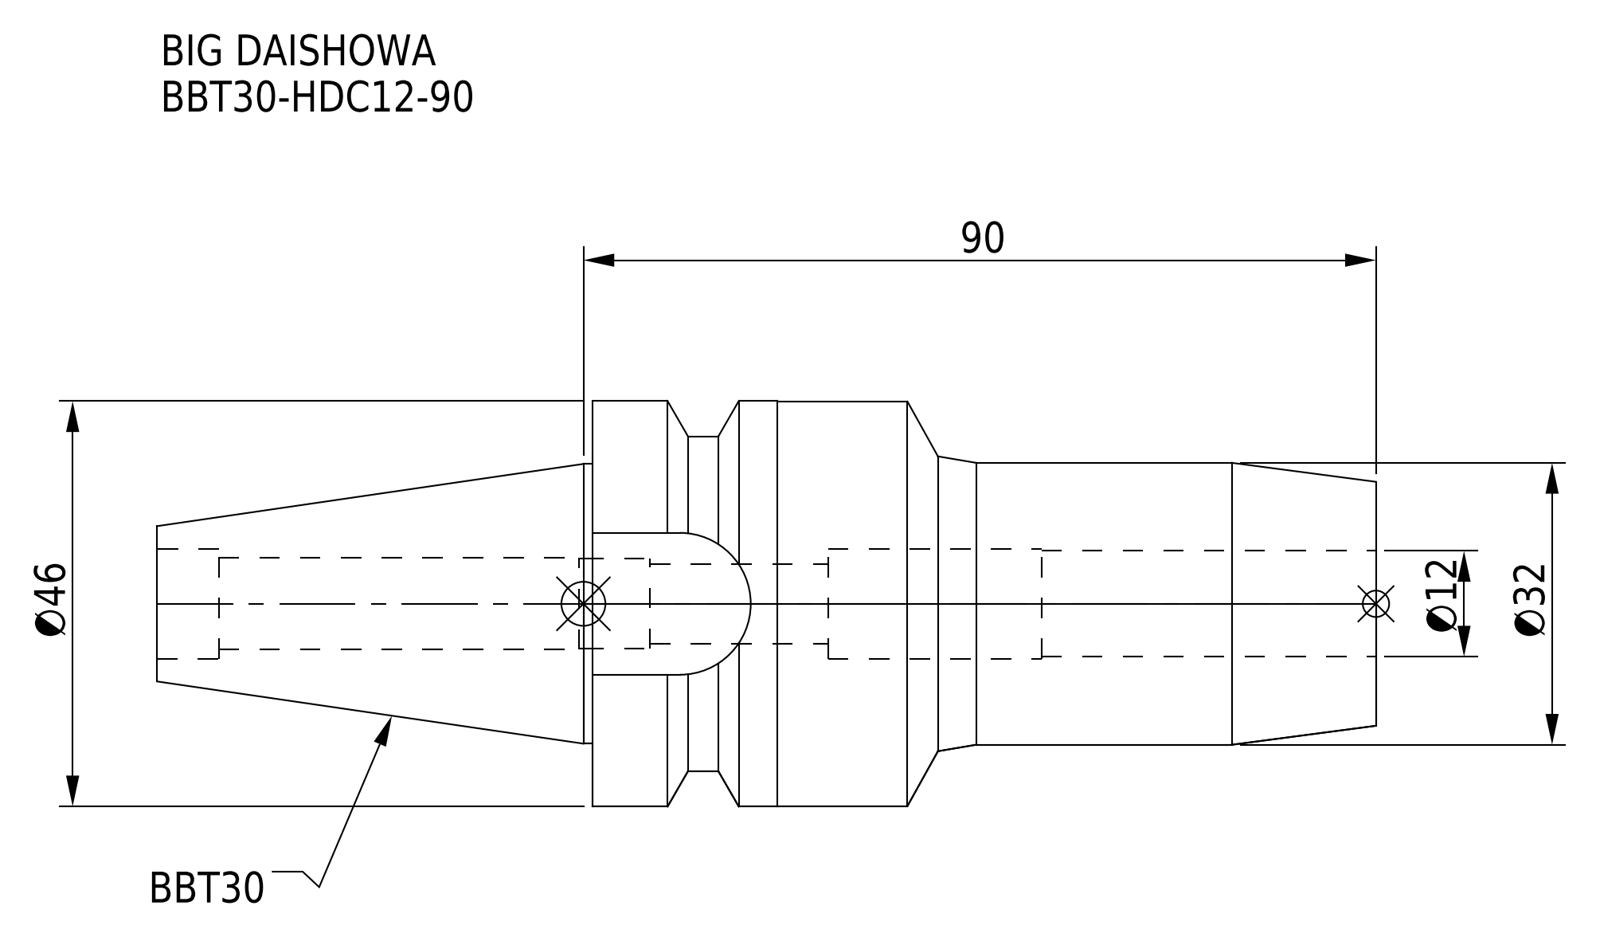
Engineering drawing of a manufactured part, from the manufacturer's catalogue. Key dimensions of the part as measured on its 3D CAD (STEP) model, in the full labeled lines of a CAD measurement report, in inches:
Part name (STEP PRODUCT): BBT30-HDC12-90
STEP written by: CREO PARAMETRIC BY PTC INC, 2016380 (AUTOMOTIVE_DESIGN)
Units: inches
Bodies: 1 solid, 55 faces (15 planar, 28 cylindrical, 12 other)
Overall size (bounding box): 5.449 × 1.811 × 1.811
Volume: 6.564 in³ · Surface area: 33.84 in²
Round holes (diameter × count): ⌀0.354 ×1, ⌀0.402 ×1, ⌀0.409 ×1, ⌀0.472 ×1, ⌀0.492 ×1
Round bosses / shafts (diameter × count): ⌀1.811 ×1, ⌀1.807 ×1, ⌀1.26 ×1, ⌀1.25 ×1
Partial cylindrical surfaces — rounded edges, fillets, slot ends (radius × count): R0.317 ×1, R0.748 ×1
Main face-to-face distances: 3.504, 1.283, 5.449, 1.945, 0.634, 2.449, 1.055, 3, 5.173, 2.724
